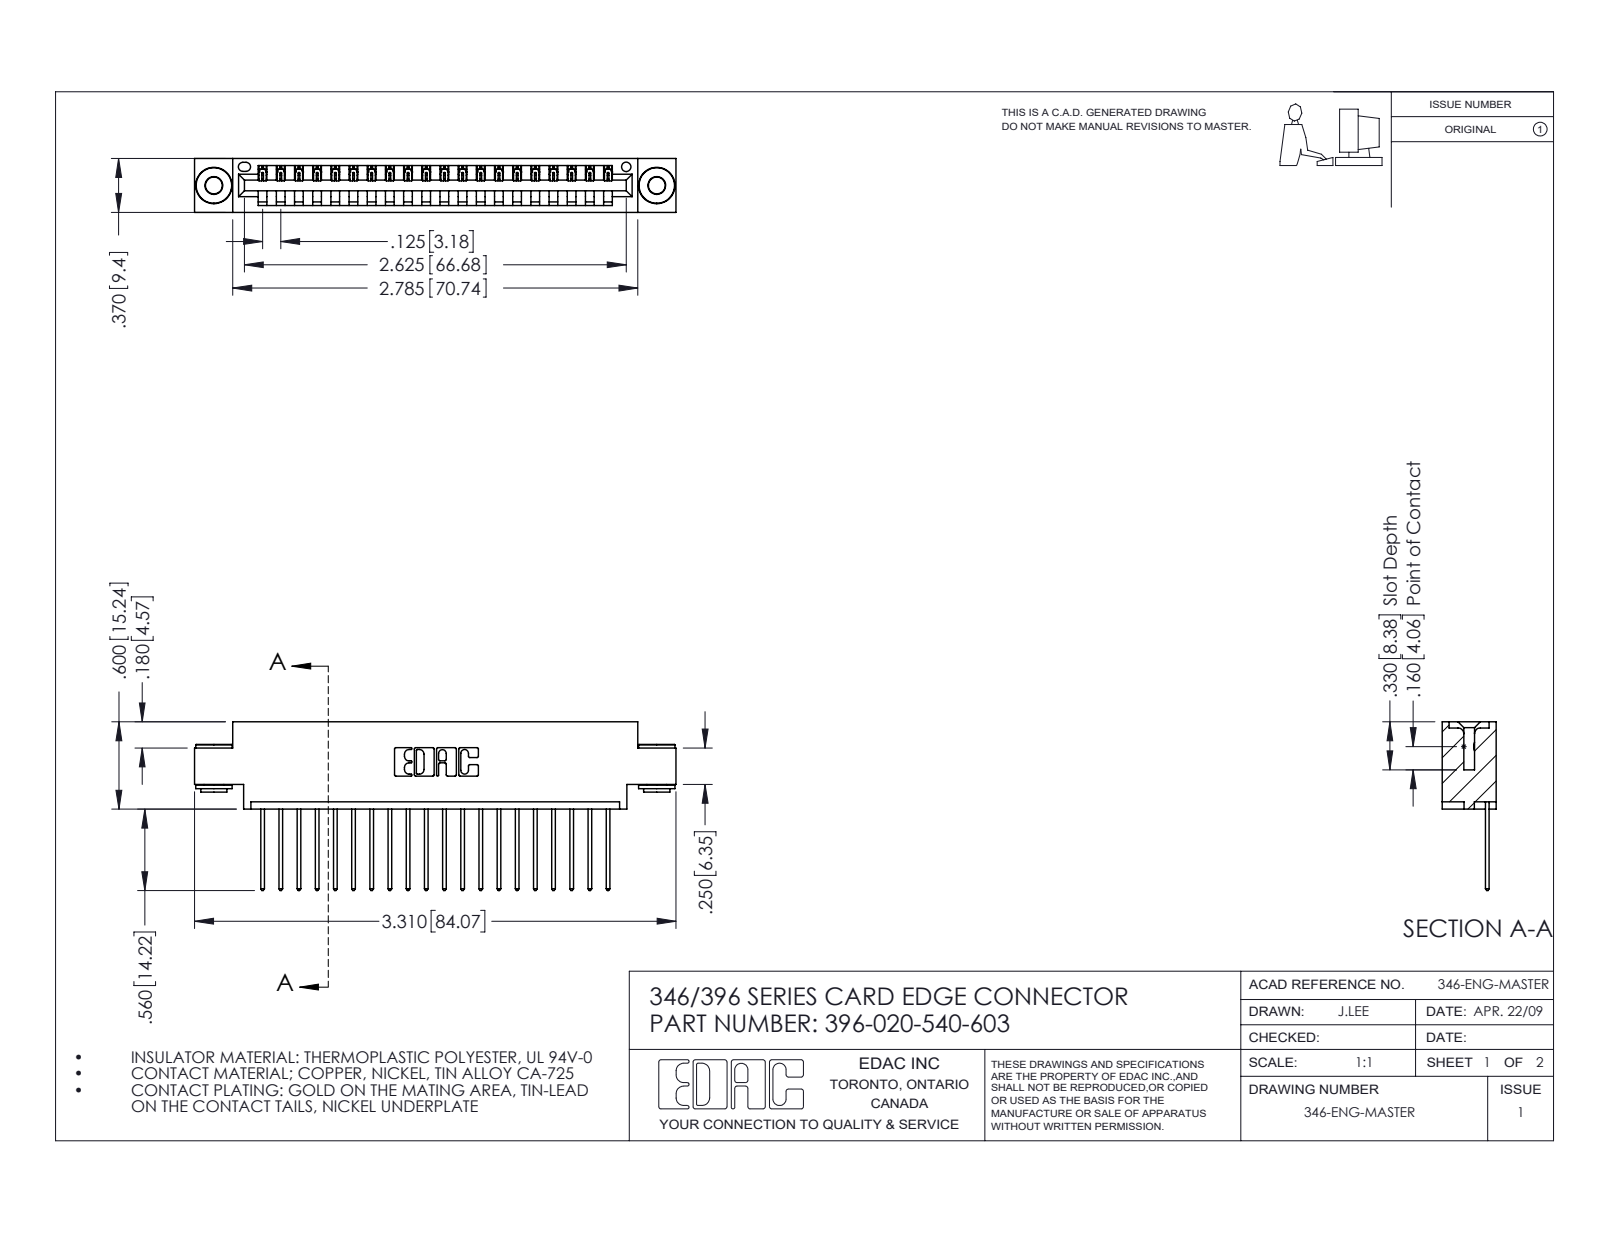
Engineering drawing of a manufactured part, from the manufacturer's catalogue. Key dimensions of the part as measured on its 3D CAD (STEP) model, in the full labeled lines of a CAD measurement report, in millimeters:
Part name (STEP PRODUCT): 396-020-540-603; 345-250-002_345-250-002-102; 345-292-001_345-293-140; 346 Part_0.170 Offset - 0.156 Dia-TH
STEP written by: SolidWorks 2016 (CONFIG_CONTROL_DESIGN)
Units: millimetres
Bodies: 23 solids, 1324 faces (890 planar, 426 cylindrical, 8 other)
Overall size (bounding box): 84.1 × 29.5 × 9.4
Volume: 7 780 mm³ · Surface area: 10 070 mm²
Round holes (diameter × count): ⌀2.9 ×2, ⌀4 ×2, ⌀1.6 ×1
Round bosses / shafts (diameter × count): ⌀6.4 ×2, ⌀4.6 ×2, ⌀3.5 ×2
Partial cylindrical surfaces — rounded edges, fillets, slot ends (radius × count): R0.2 ×40, R0.3 ×40, R0.3 ×22, R0.2 ×6, R0.8 ×6, R0.7 ×3, R0.8 ×2, R1 ×2
Main face-to-face distances: 1.2, 8.2, 9.4, 6.4, 0.6, 1.8, 7.6, 3.8, 5.6, 2.5
Hole centre spacings: 6.2, 72.1, 77.3
